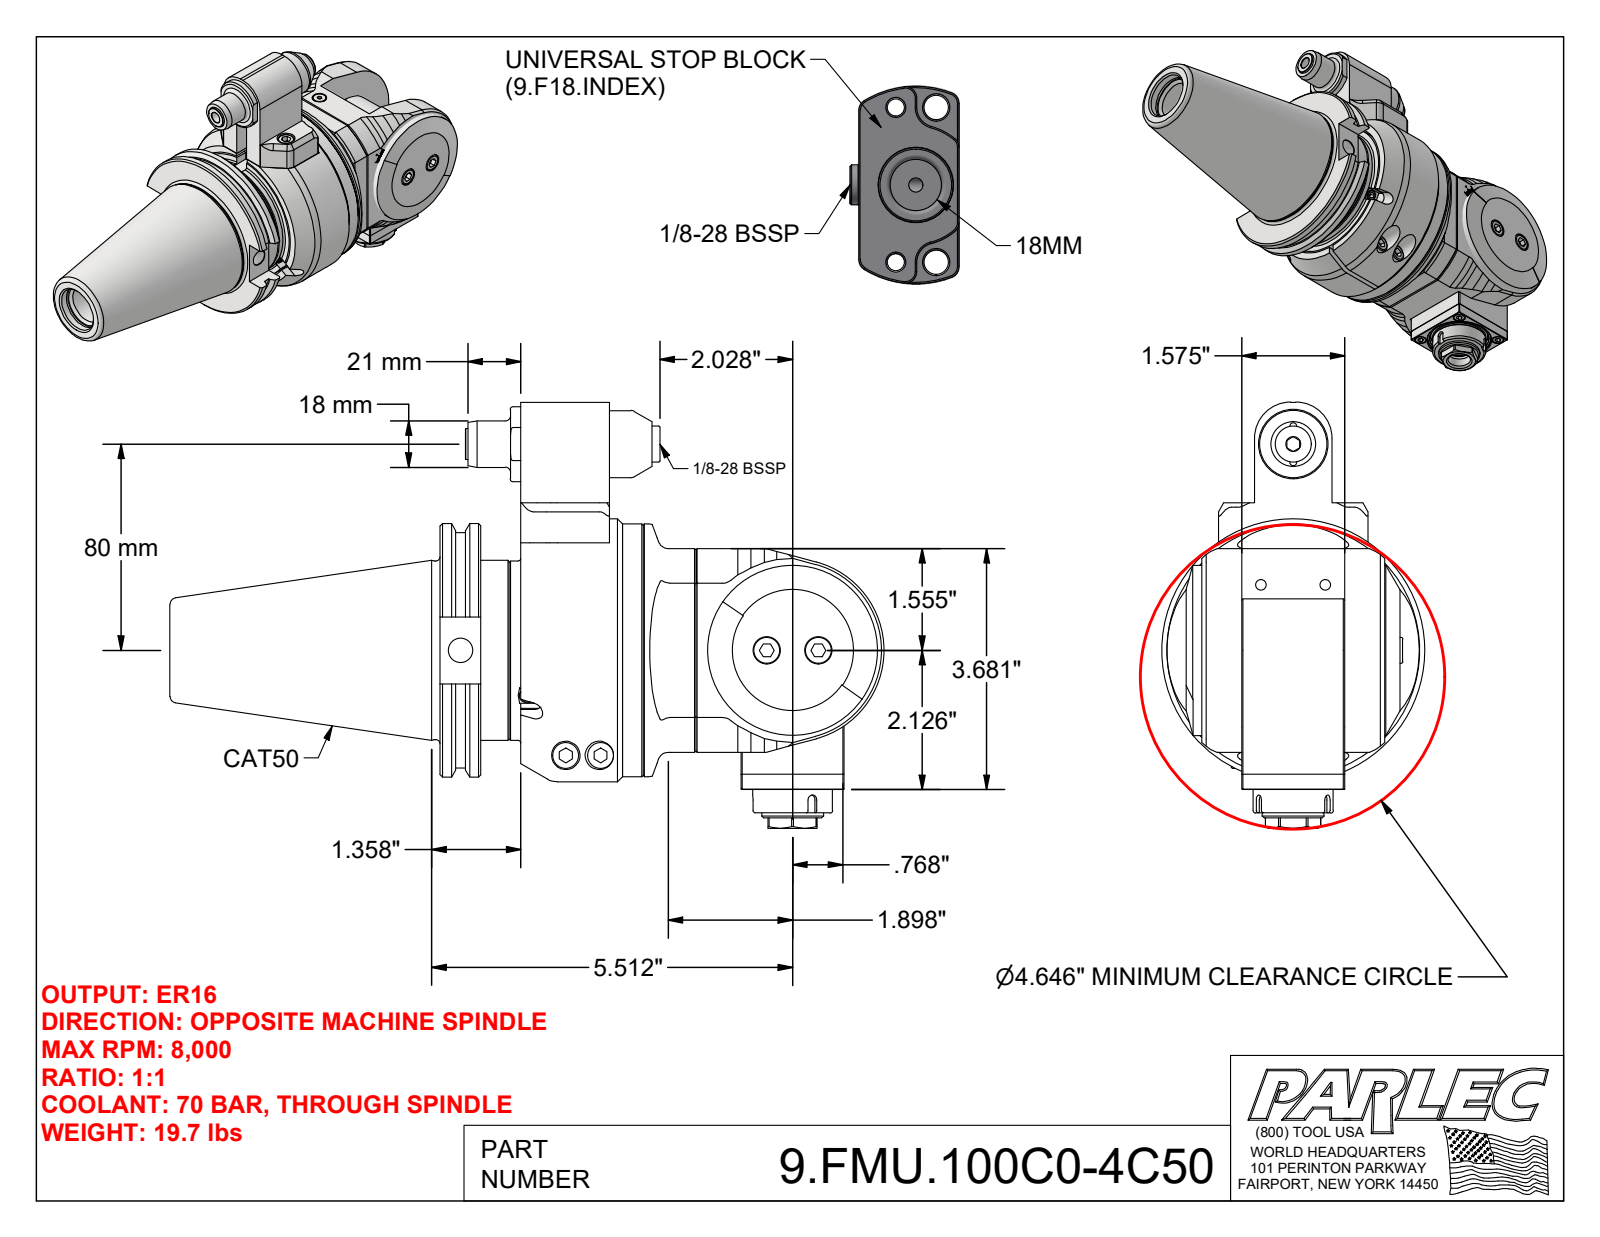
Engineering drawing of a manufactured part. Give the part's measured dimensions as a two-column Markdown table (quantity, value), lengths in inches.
| quantity | value |
| --- | --- |
| part name | 9.FMU.100C0-4C50; 9_GA1_458_2 (Type 1, Cat50, 80mm); FMU-10C |
| STEP written by | Autodesk Inventor 2022 (AUTOMOTIVE_DESIGN) |
| units | inches |
| bodies | 6 solids, 627 faces (318 planar, 133 cylindrical, 176 other) |
| overall size | 10.909 × 6.506 × 4.016 |
| volume | 79.57 in³ |
| surface area | 296.8 in² |
| round holes (diameter × count) | 0.276 × 5, 0.413 × 3, 0.433 × 3, 0.102 × 2, 0.157 × 2, 0.197 × 2, 0.409 × 2, 0.098 × 1, 0.118 × 1, 0.256 × 1, 0.335 × 1, 0.375 × 1 |
| round bosses / shafts (diameter × count) | 0.394 × 7, 0.236 × 6, 0.709 × 2, 0.315 × 2, 4.016 × 1, 3.875 × 1, 3.858 × 1, 3.594 × 1 |
| partial cylindrical surfaces (radius × count) | 0.157 × 6, 0.079 × 3, 0.02 × 2, 0.039 × 2, 0.138 × 2, 0.197 × 2, 0.551 × 2, 0.423 × 1 |
| main face-to-face distances | 0.531, 1.26, 1.575, 2.106, 0.61, 2.185, 2.717, 3.031, 0.846, 1.791 |
| hole center spacings | 0.886, 1.253, 0.276, 0.394, 0.872, 0.9, 1.118, 1.772 |
